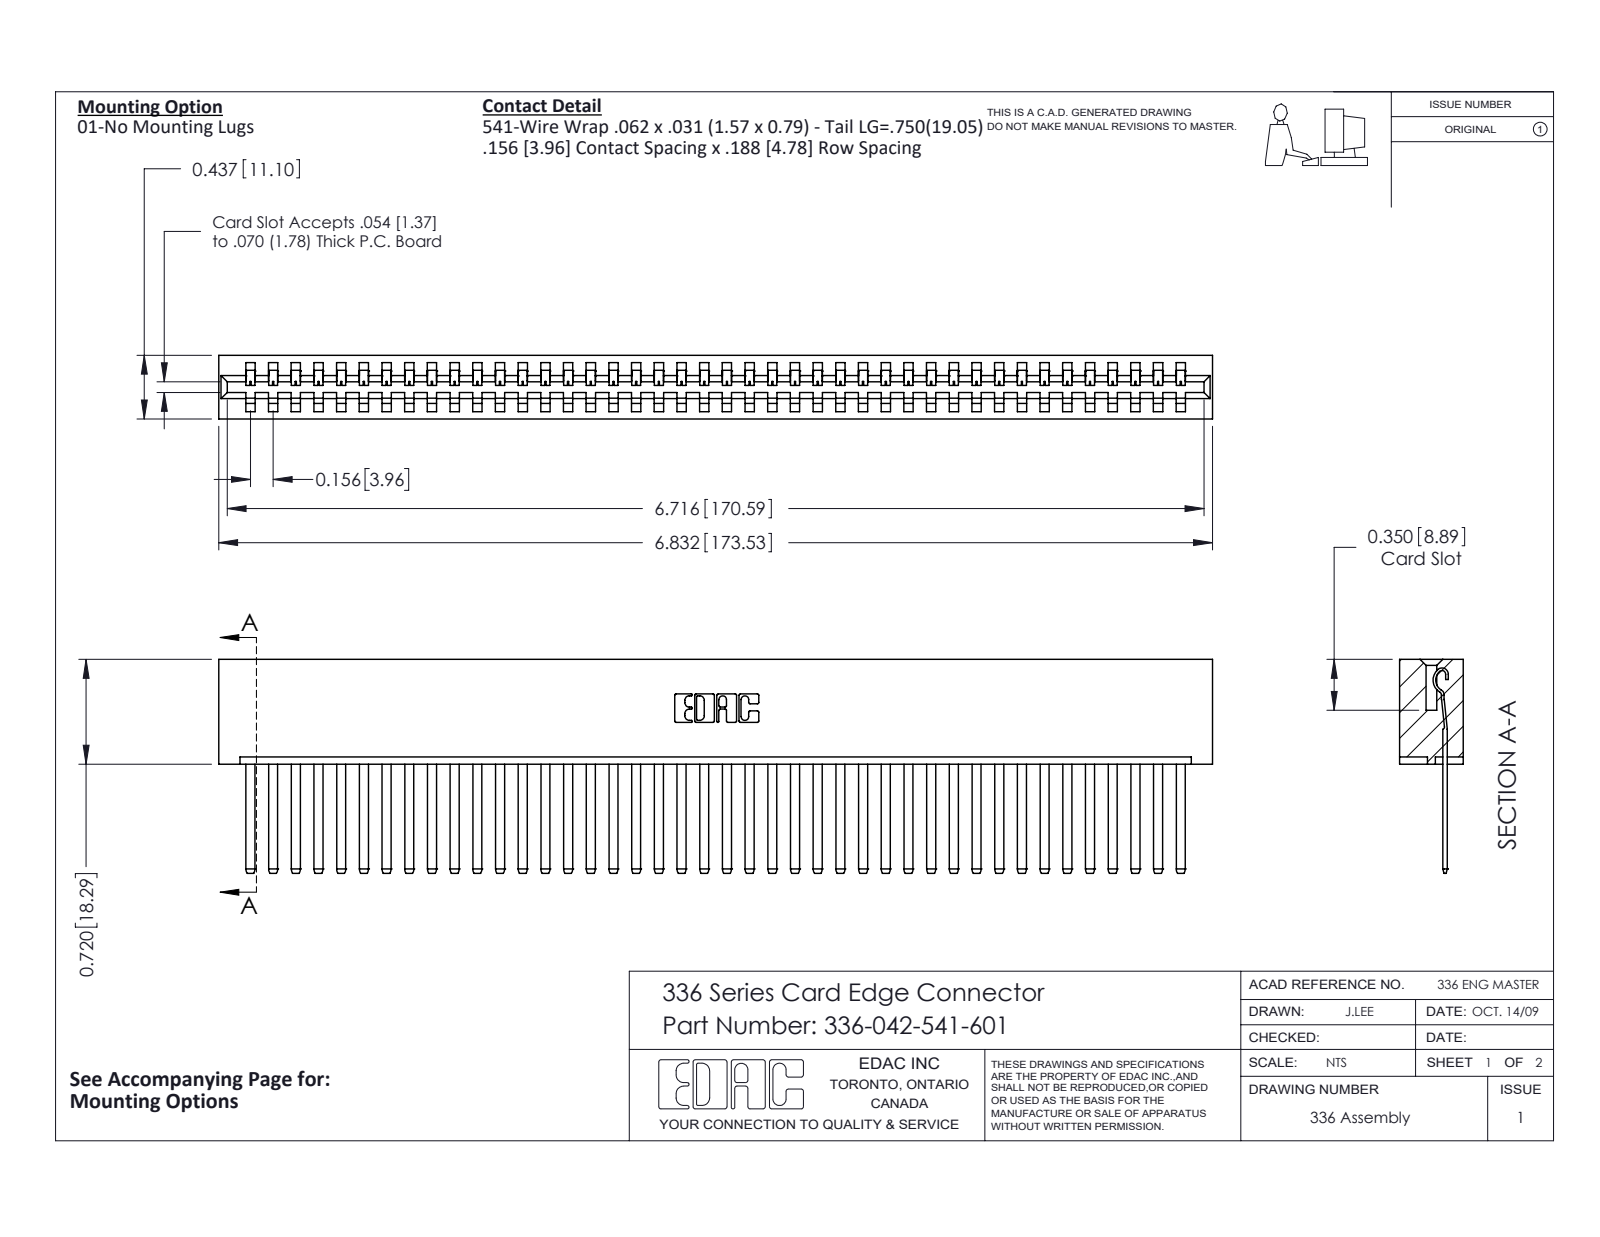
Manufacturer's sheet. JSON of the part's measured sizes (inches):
{"part_name": "336 Part_Lugless; 336-290-001_336-290-541; 336-042-541-601", "step_written_by": "SolidWorks 2020 (CONFIG_CONTROL_DESIGN)", "units": "inches", "bodies": {"solids": 43, "faces": 2206, "planar": 1494, "cylindrical": 712, "other": 0}, "overall_size": [6.832, 1.47, 0.437], "volume_in3": 1.637, "surface_area_in2": 45.3, "partial_cylinders_radius": [[0.004, 84], [0.056, 84], [0.01, 22], [0.007, 6], [0.031, 6], [0.026, 3], [0.022, 2], [0.04, 2]], "face_to_face_distances": [0.437, 0.181, 0.328, 0.14, 0.297, 0.109, 0.031, 0.256, 0.05, 0.387]}
